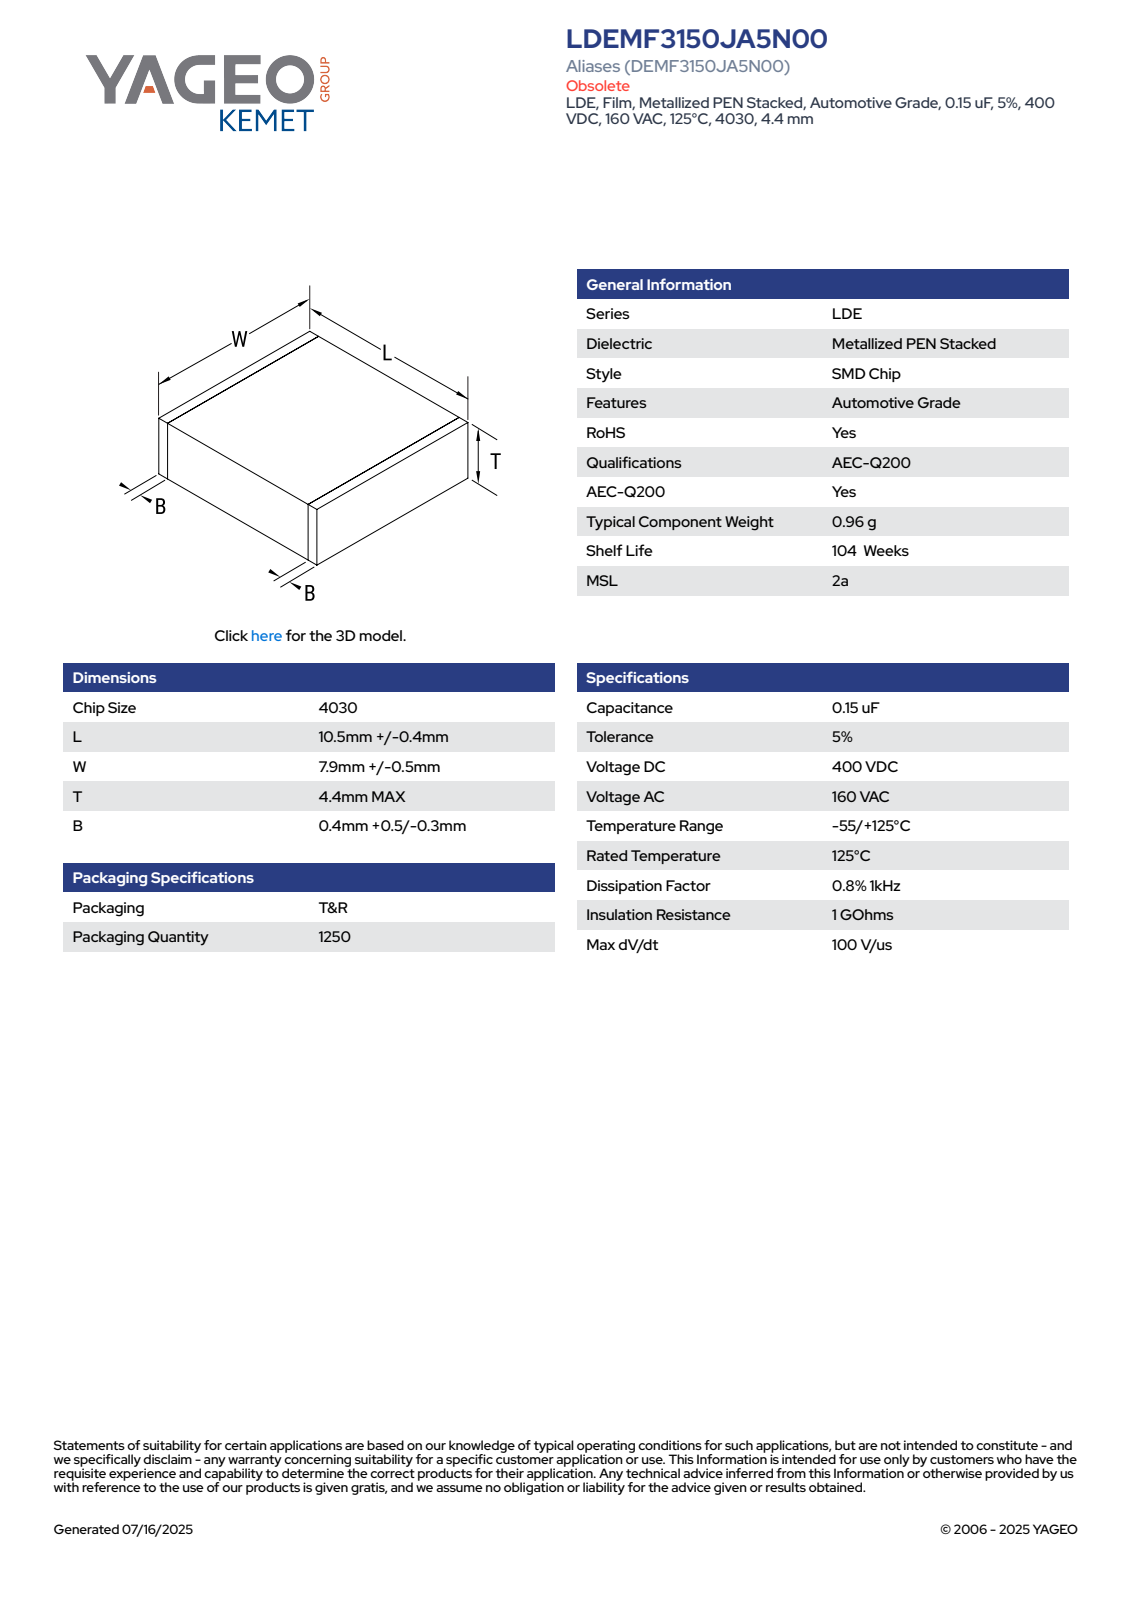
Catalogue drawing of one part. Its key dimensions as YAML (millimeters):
part_name: "CFS_LDELDB_4030_L10.9W8.4T4.4B0.9"
step_written_by: "SolidWorks 2020 (AUTOMOTIVE_DESIGN)"
units: millimeters
bodies: {solids: 4, faces: 73, planar: 73, cylindrical: 0, other: 0}
overall_size: [10.9, 8.4, 4.4]
volume: 400
surface_area: 358
face_to_face_distances: [4.38, 8.38, 10.9, 4.39, 8.39, 4.4, 8.4, 0.5, 10.4, 9.9]
